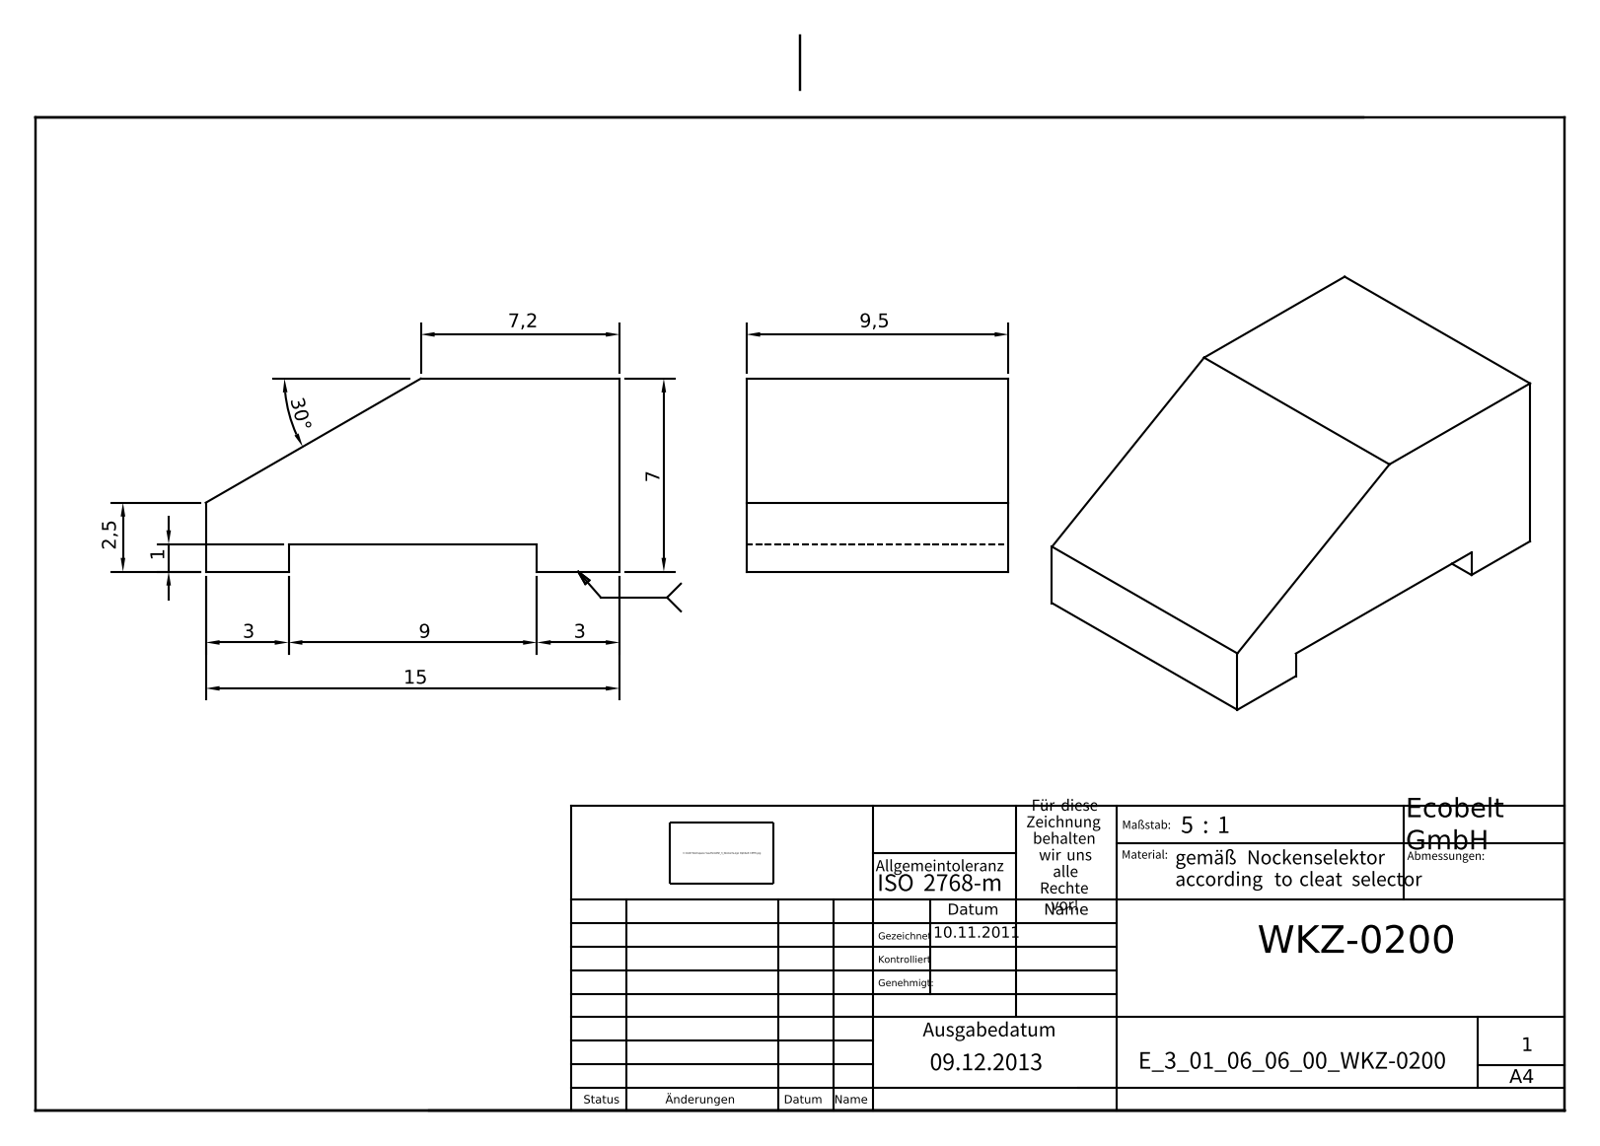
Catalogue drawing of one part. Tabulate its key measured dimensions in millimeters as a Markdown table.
| quantity | value |
| --- | --- |
| part name | E_3_01_06_06_00_WKZ-0200 |
| STEP written by | Autodesk Inventor 2025 (AUTOMOTIVE_DESIGN) |
| units | millimeters |
| bodies | 1 solid, 11 faces (11 planar, 0 cylindrical, 0 other) |
| overall size | 15 × 9.5 × 7 |
| volume | 745 mm³ |
| surface area | 563 mm² |
| main face-to-face distances | 9.5, 6, 1, 7, 15, 3, 12, 9 |
